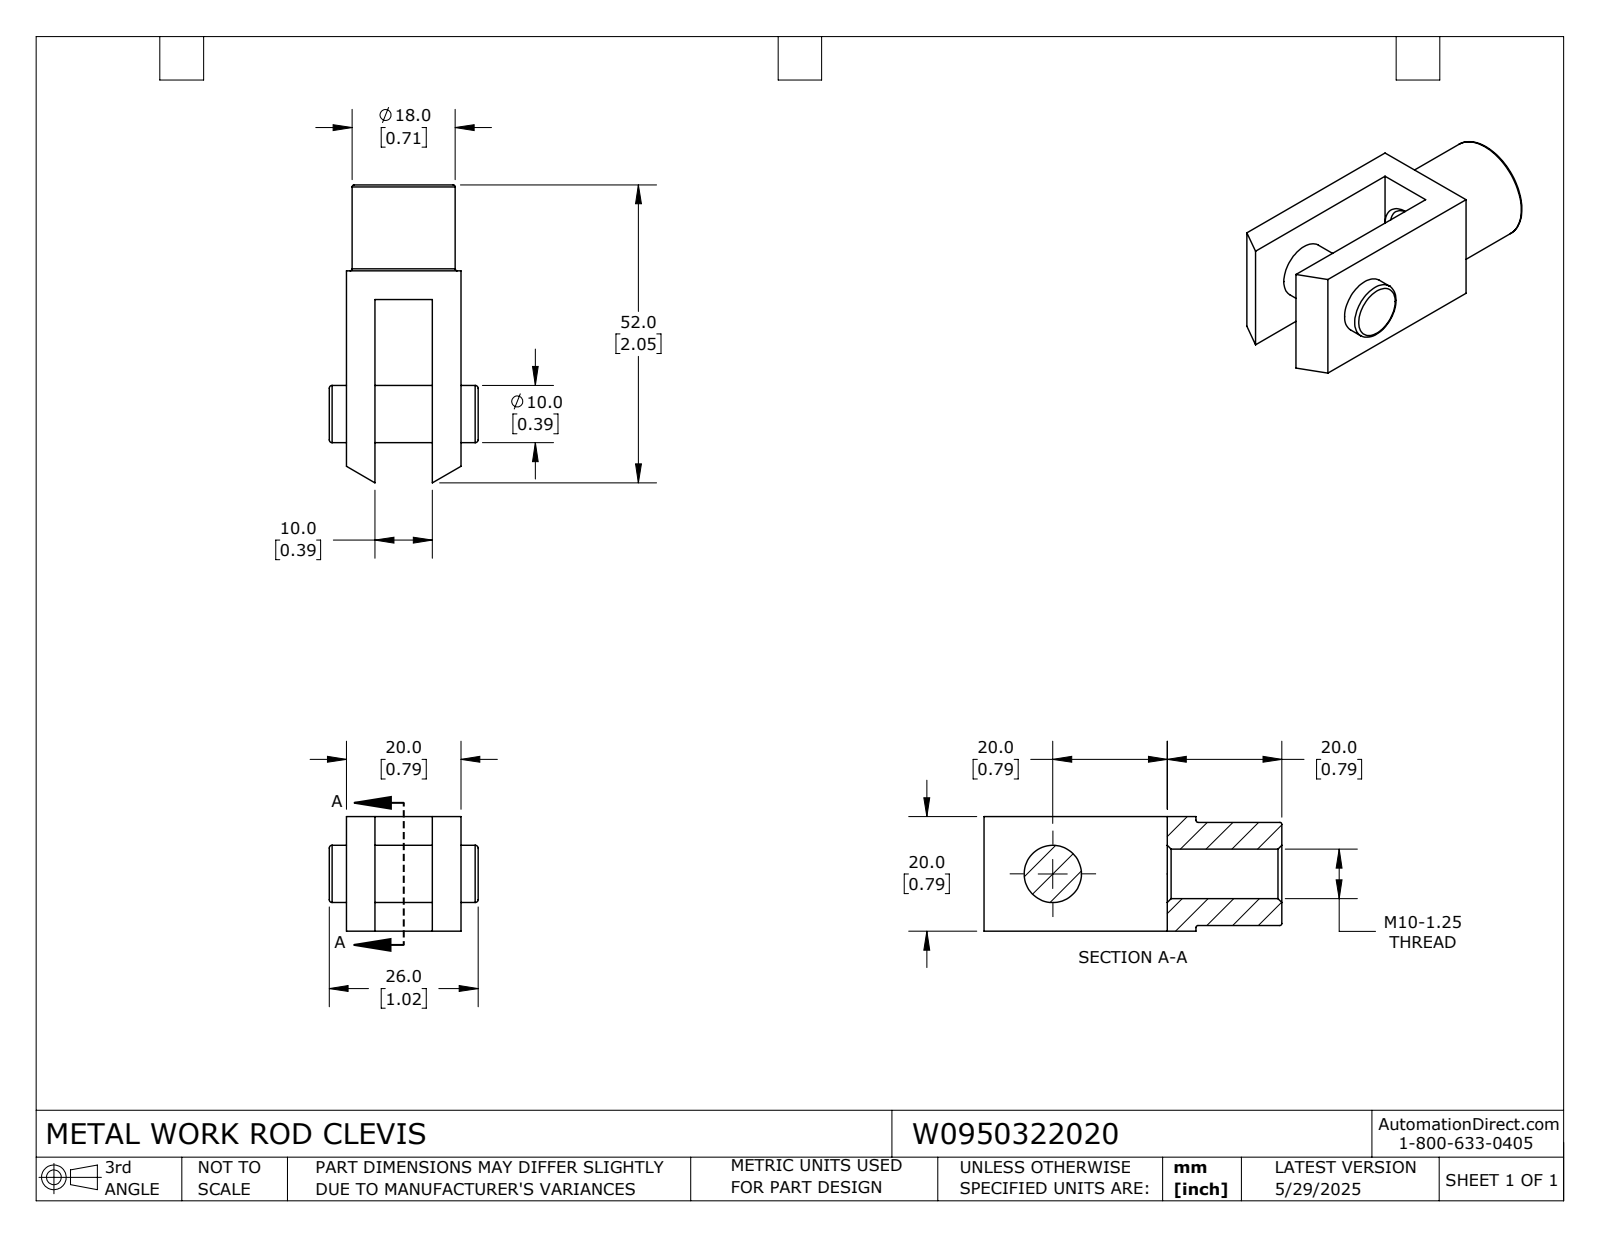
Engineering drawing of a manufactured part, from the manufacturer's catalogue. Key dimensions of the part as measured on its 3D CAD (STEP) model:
Part name (STEP PRODUCT): W0950322020
STEP written by: SolidWorks 2024 (CONFIG_CONTROL_DESIGN)
Units: millimetres
Bodies: 1 solid, 36 faces (14 planar, 10 cylindrical, 12 other)
Overall size (bounding box): 52 × 26 × 20
Volume: 11 994 mm³ · Surface area: 5 855 mm²
Round holes (diameter × count): ⌀8.65 ×1
Round bosses / shafts (diameter × count): ⌀18 ×1, ⌀10 ×1
Main face-to-face distances: 15, 5, 20, 10, 3, 8, 18, 23, 26
